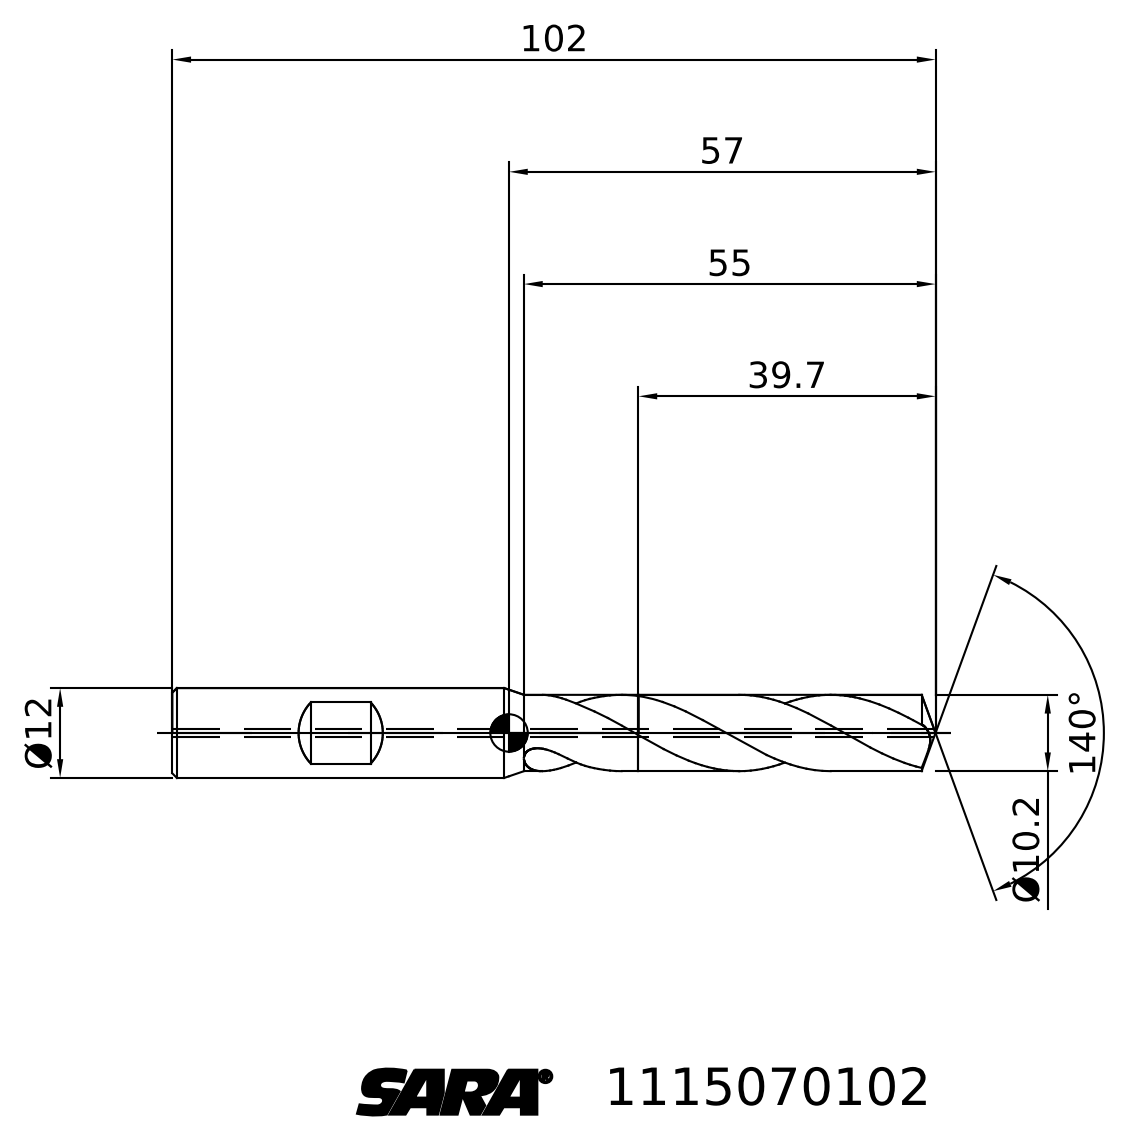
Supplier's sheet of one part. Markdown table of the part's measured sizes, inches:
| quantity | value |
| --- | --- |
| STEP written by | TDM (AUTOMOTIVE_DESIGN) |
| units | inches |
| bodies | 2 solids, 30 faces (6 planar, 0 cylindrical, 24 other) |
| overall size | 4.016 × 1.059 × 0.617 |
| volume | 0.498 in³ |
| surface area | 6.043 in² |
| main face-to-face distances | 2.453 |
